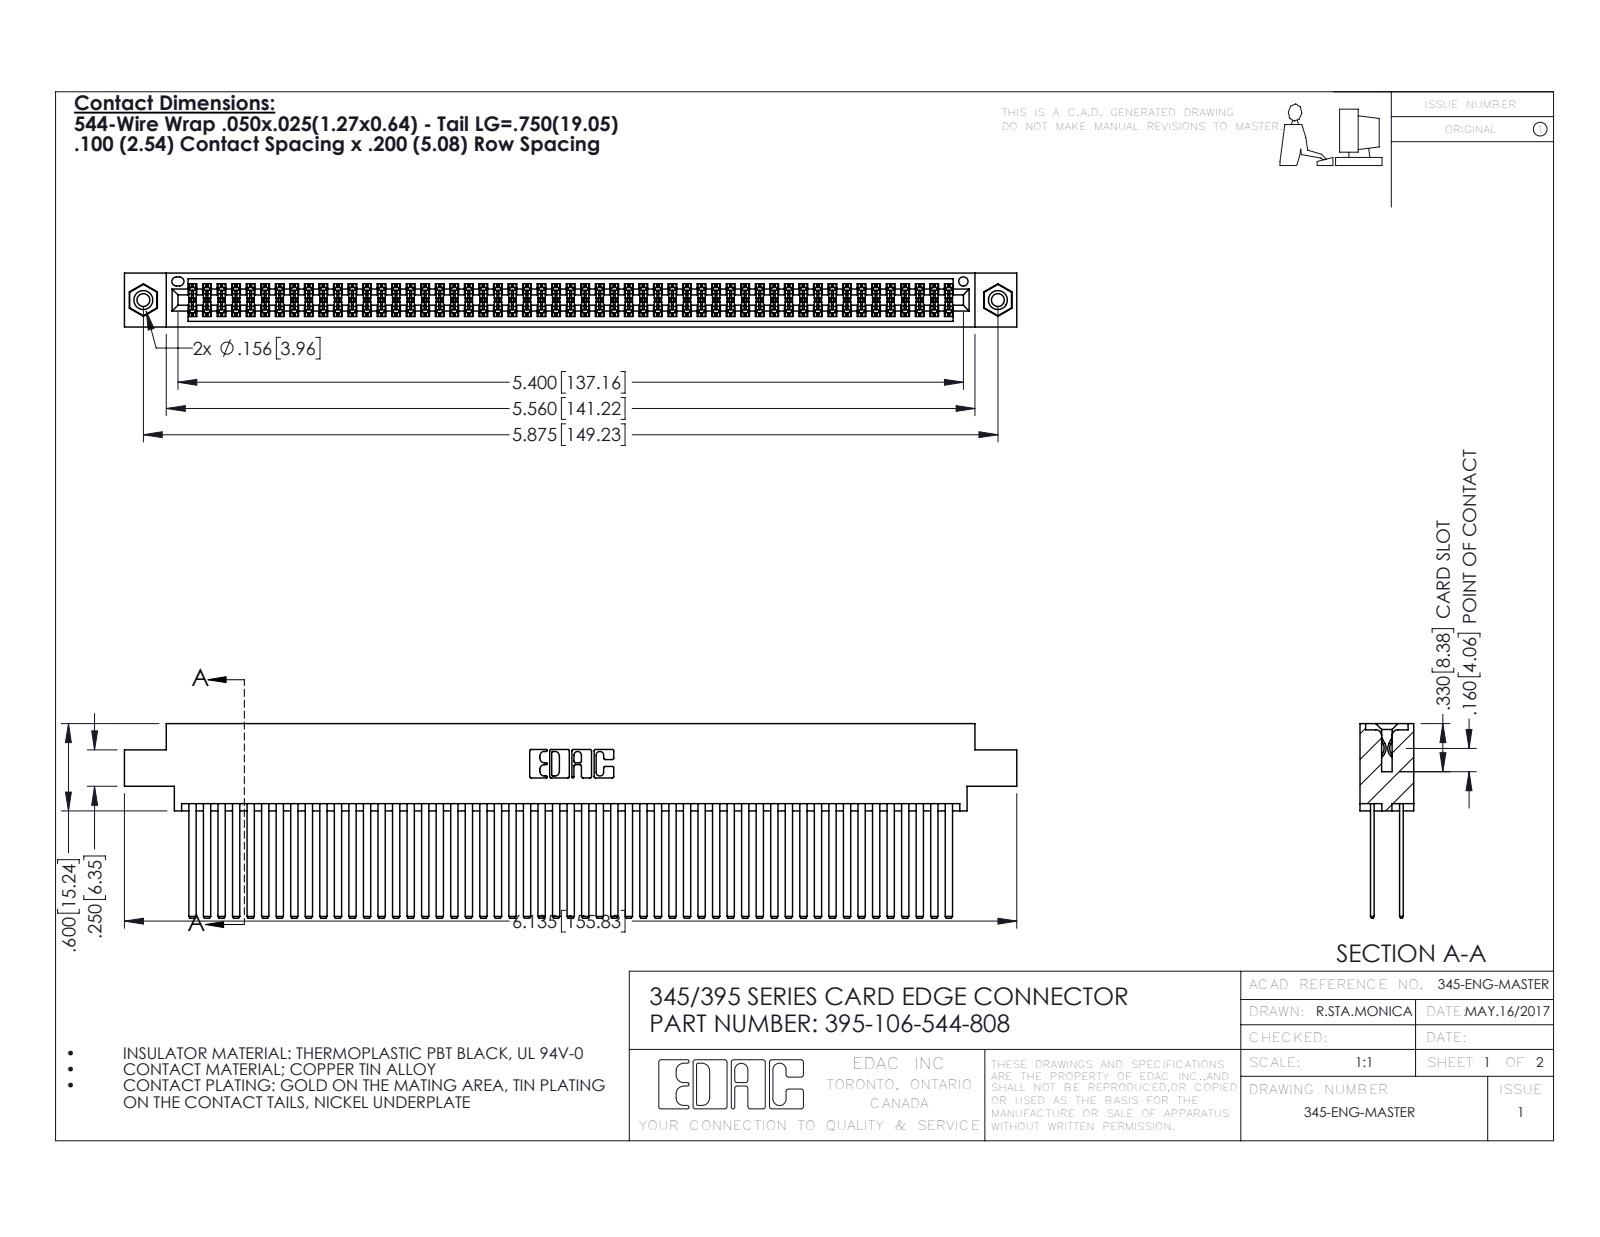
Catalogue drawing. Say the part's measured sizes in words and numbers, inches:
The part is named "345 Part_0.170 Offset - 0.156 Dia-TI; 345-292-001_345-293-144; 345-250-001_345-250-003-102; 395-106-544-808". Its 3-D file was written by "SolidWorks 2016 (CONFIG_CONTROL_DESIGN)". It is 109 solids with 4854 faces: 3190 planar, 1648 cylindrical and 16 other. Overall it measures 6.135 by 1.337 by 0.37 inches. Its volume is 1.013 cubic inches and its surface area 45.37 square inches. Round holes: 2 of diameter 0.089, 2 of diameter 0.125, 2 of diameter 0.156, 1 of diameter 0.064. Round bosses or shafts: 2 of diameter 0.155. Partial cylindrical surfaces (rounded edges, fillets, slot ends): 159 of radius 0.006, 22 of radius 0.01, 6 of radius 0.007, 6 of radius 0.031, 3 of radius 0.026, 2 of radius 0.014, 2 of radius 0.019, 2 of radius 0.022. The main face-to-face distances are 0.2, 0.025, 0.072, 0.098, 0.272, 0.298, 0.225, 0.175, 0.37, 0.15. The hole center spacings are 0.27, 5.639, 5.875.
